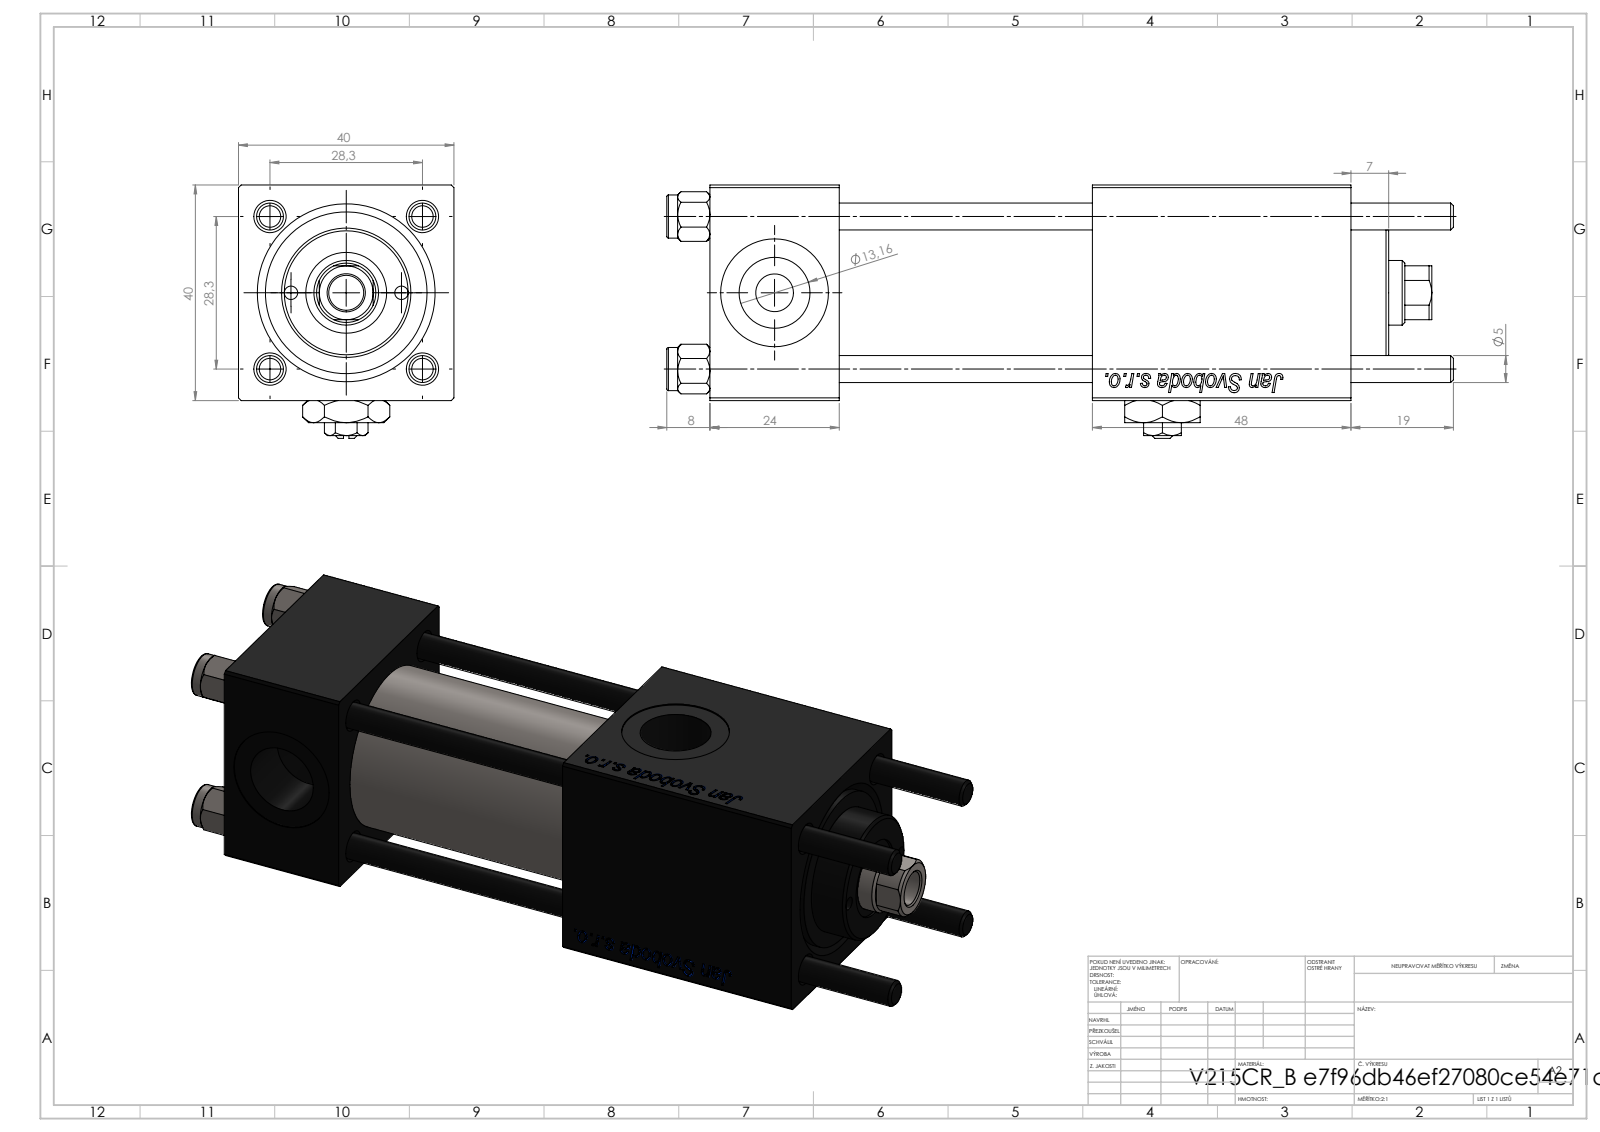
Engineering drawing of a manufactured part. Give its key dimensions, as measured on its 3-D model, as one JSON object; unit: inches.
{"part_name": "V215CR_B_TYCINKA; Zatka_pro_OIL_PORT; V215_VC_A; NUT_M5_B (+2 more)", "step_written_by": "SolidWorks 2019 (CONFIG_CONTROL_DESIGN)", "units": "inches", "bodies": {"solids": 12, "faces": 1209, "planar": 455, "cylindrical": 86, "other": 668}, "overall_size": [5.748, 1.85, 1.575], "volume_in3": 8.795, "surface_area_in2": 92.29, "round_holes": [[0.197, 4], [0.787, 4], [0.518, 3], [0.098, 2], [0.276, 2], [0.256, 1], [0.472, 1], [0.591, 1], [0.984, 1], [1.181, 1]], "round_bosses_or_shafts": [[0.315, 4], [1.22, 1], [0.945, 1]], "partial_cylinders_radius": [[0.217, 1]], "face_to_face_distances": [1.575, 0.945, 3.555, 2.61, 1.85, 0.76, 2.795, 1.89, 4.685, 3.74], "hole_center_spacings": [0.578, 0.788, 1.111, 1.114, 0.404, 1.576, 0.807]}
